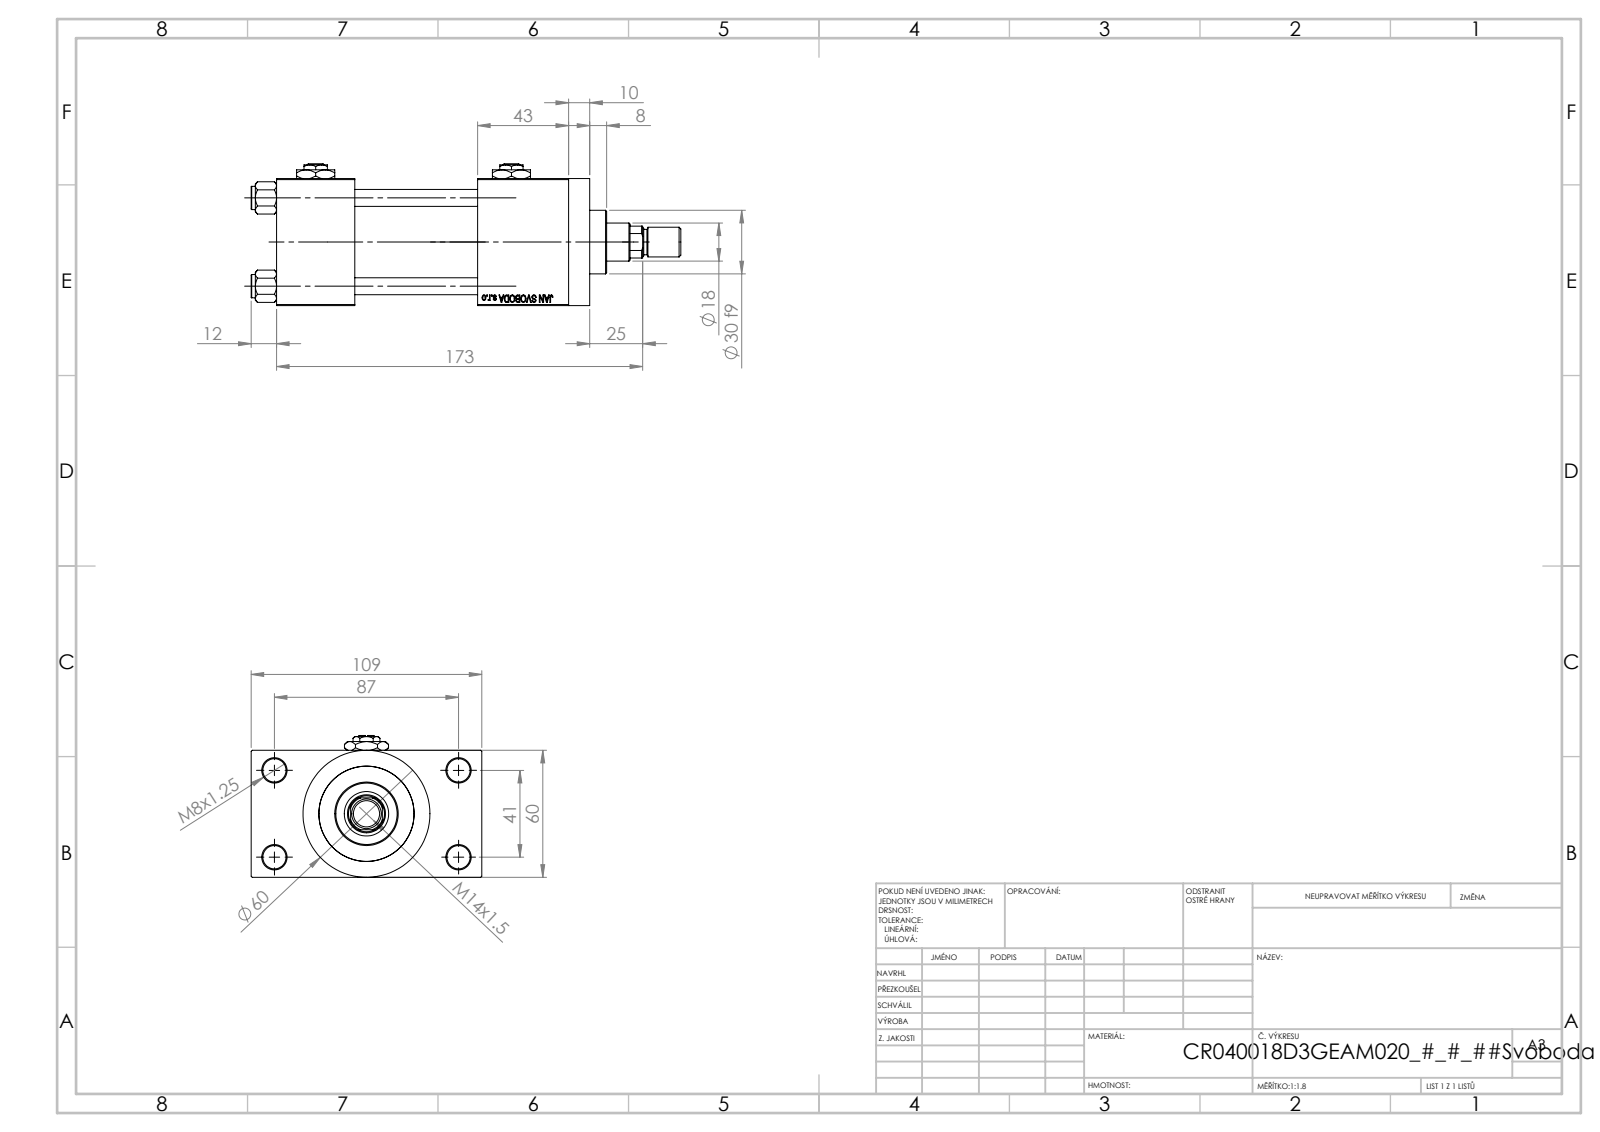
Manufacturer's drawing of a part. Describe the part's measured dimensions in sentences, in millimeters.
The part is named "V215CR_D_TYCINKA; ROD_END_AH; V215CR_VCP_D; V215_VC_A (+3 more)". Its 3-D file was written by "SolidWorks 2019 (CONFIG_CONTROL_DESIGN)". It is 14 solids with 1220 faces: 550 planar, 104 cylindrical and 566 other. Overall it measures 203 by 109 by 67 millimeters. Its volume is 518 264 cubic millimeters and its surface area 125 041 square millimeters. Round holes: 4 of diameter 8, 4 of diameter 11, 2 of diameter 7, 2 of diameter 16.66, 2 of diameter 24, 1 of diameter 8.5, 1 of diameter 18, 1 of diameter 21, 1 of diameter 31, 1 of diameter 40, 1 of diameter 45. Round bosses or shafts: 4 of diameter 11, 1 of diameter 60, 1 of diameter 46, 1 of diameter 30, 1 of diameter 14, 1 of diameter 12. Partial cylindrical surfaces (rounded edges, fillets, slot ends): 1 of radius 8.5. The main face-to-face distances are 60, 24.5, 84.5, 58, 37, 95, 43, 138, 101, 109. The hole center spacings are 22.65, 29.49, 41.7, 47.15, 48.09, 64.35, 76.49, 41.
